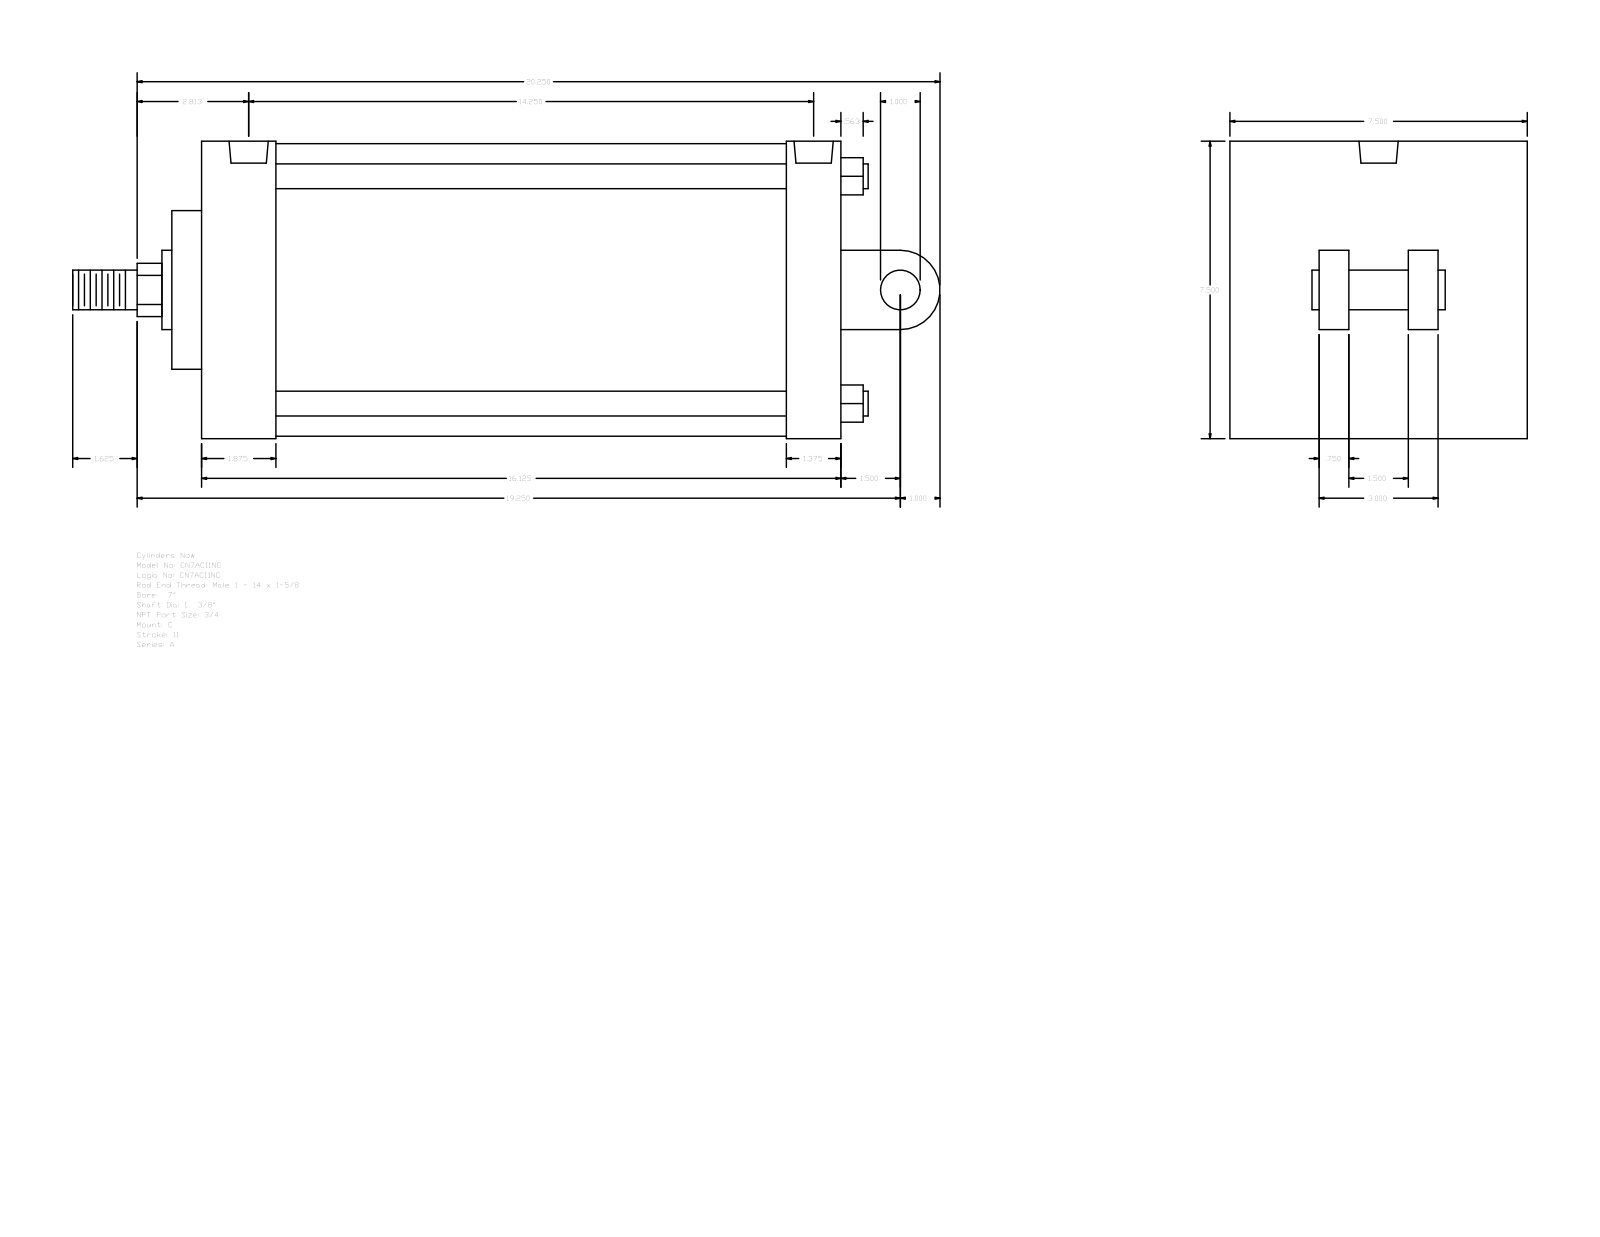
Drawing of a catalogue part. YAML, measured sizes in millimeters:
part_name: "A_C__0700_1.375"
step_written_by: "GSSL Pune (CONFIG_CONTROL_DESIGN)"
units: millimeters
bodies: {solids: 0, faces: 104, planar: 75, cylindrical: 29, other: 0}
overall_size: [555.62, 190.5, 190.5]
round_holes:
  - {diameter: 15.08, count: 4}
  - {diameter: 25.12, count: 2}
round_bosses_or_shafts:
  - {diameter: 15.88, count: 4}
  - {diameter: 25.4, count: 2}
  - {diameter: 187.32, count: 1}
  - {diameter: 50.8, count: 1}
  - {diameter: 34.92, count: 1}
partial_cylinders:
  - {radius: 17.06, count: 1}
  - {radius: 25.4, count: 1}
face_to_face_distances: [190.5, 409.58, 76.2, 57.15, 19.04, 428.62, 66.67, 47.63, 361.95, 393.7]
hole_center_spacings: [5.56, 350.83, 356.39, 361.95]
